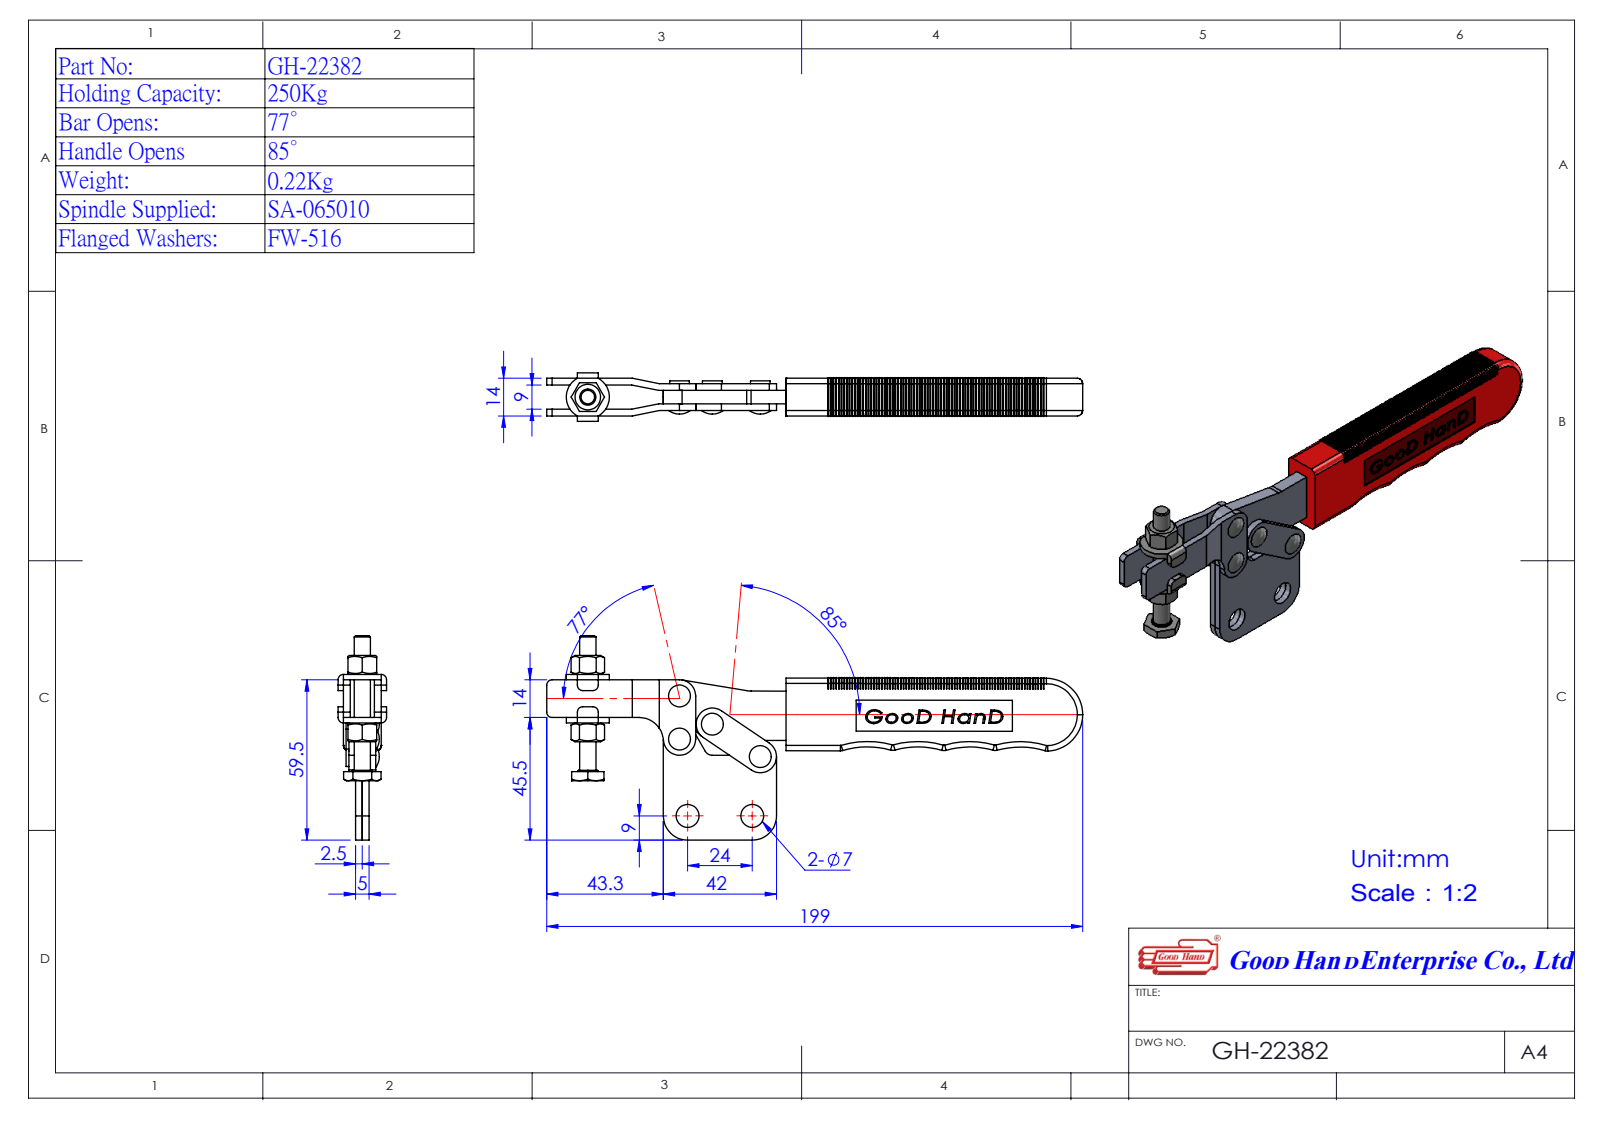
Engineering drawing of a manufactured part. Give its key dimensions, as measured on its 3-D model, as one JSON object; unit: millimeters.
{"part_name": "Group4^GH-22382(簡化); GH-22382(簡化)-1; Group1^GH-22382(簡化)-1; Group2^GH-22382(簡化)-1 (+2 more)", "step_written_by": "SolidWorks 2016 (AUTOMOTIVE_DESIGN)", "units": "millimeters", "bodies": {"solids": 5, "faces": 232, "planar": 104, "cylindrical": 106, "other": 22}, "overall_size": [198.99, 75.9, 18], "volume_mm3": 61017, "surface_area_mm2": 24999, "round_holes": [[5, 5], [8.5, 2]], "round_bosses_or_shafts": [[7.3, 4], [12, 1], [7.5, 1], [6, 1]], "partial_cylinders_radius": [[2, 10], [3, 9], [1, 4], [32, 4], [6, 3], [8, 1], [9, 1], [10, 1]], "face_to_face_distances": [9.5, 4.5, 14, 5, 2, 2.5, 12, 7.5, 11.5, 7], "hole_center_spacings": [13.38, 16, 16.06, 21.5, 22.2, 24, 28.66, 30.7]}
